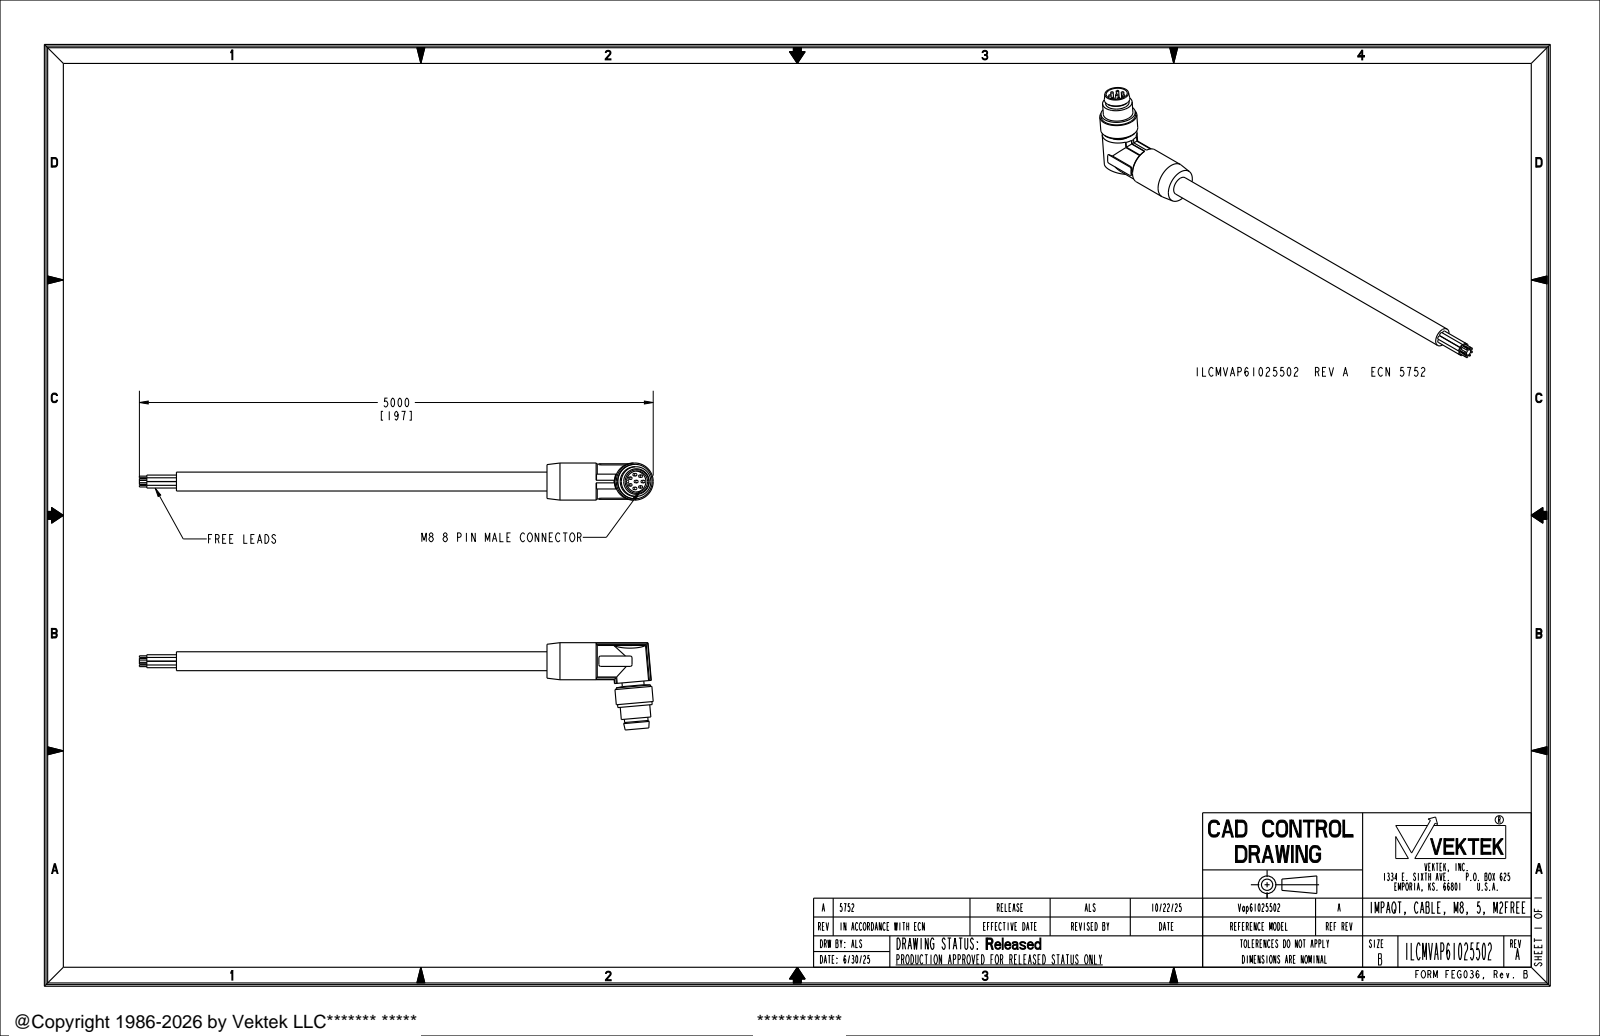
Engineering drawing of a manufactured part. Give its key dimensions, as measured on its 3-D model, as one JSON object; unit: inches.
{"part_name": "ILCMVAP61025502", "step_written_by": "CREO PARAMETRIC BY PTC INC, 2021164 (AUTOMOTIVE_DESIGN)", "units": "inches", "bodies": {"solids": 1, "faces": 163, "planar": 57, "cylindrical": 95, "other": 11}, "overall_size": [5.459, 0.927, 0.394], "volume_in3": 0.295, "surface_area_in2": 5.453, "round_holes": [[0.224, 1]], "round_bosses_or_shafts": [[0.039, 8], [0.026, 8], [0.017, 8], [0.394, 2], [0.366, 1], [0.315, 1], [0.25, 1], [0.232, 1]], "partial_cylinders_radius": [[0.02, 4], [0.185, 2], [0.193, 2], [0.013, 1]], "face_to_face_distances": [0.378, 0.304, 0.161, 0.083, 0.387, 0.11, 0.13, 0.047, 0.257, 0.079]}
